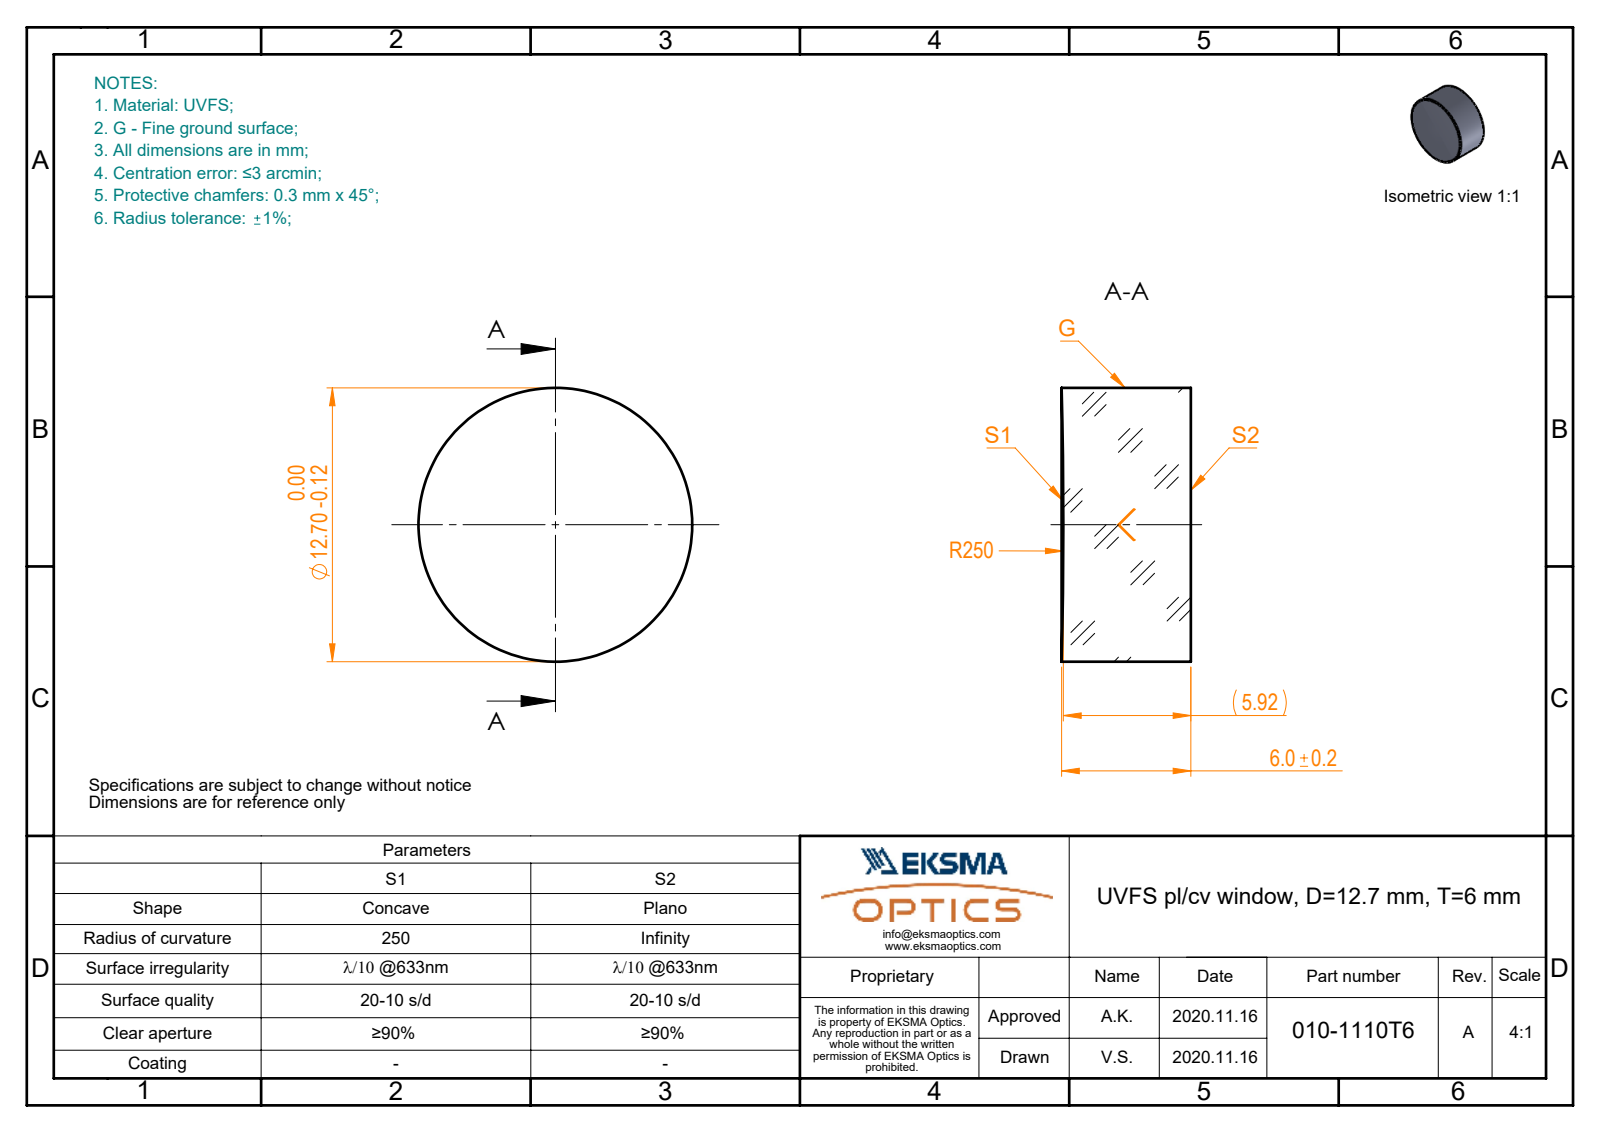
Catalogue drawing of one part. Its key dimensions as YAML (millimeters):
part_name: "010-1110T6_UVFS_PCV_window"
step_written_by: "SolidWorks 2019 (CONFIG_CONTROL_DESIGN)"
units: millimeters
bodies: {solids: 1, faces: 5, planar: 1, cylindrical: 2, other: 2}
overall_size: [12.7, 12.7, 6]
volume: 755
surface_area: 493
round_bosses_or_shafts:
  - {diameter: 12.7, count: 1}
